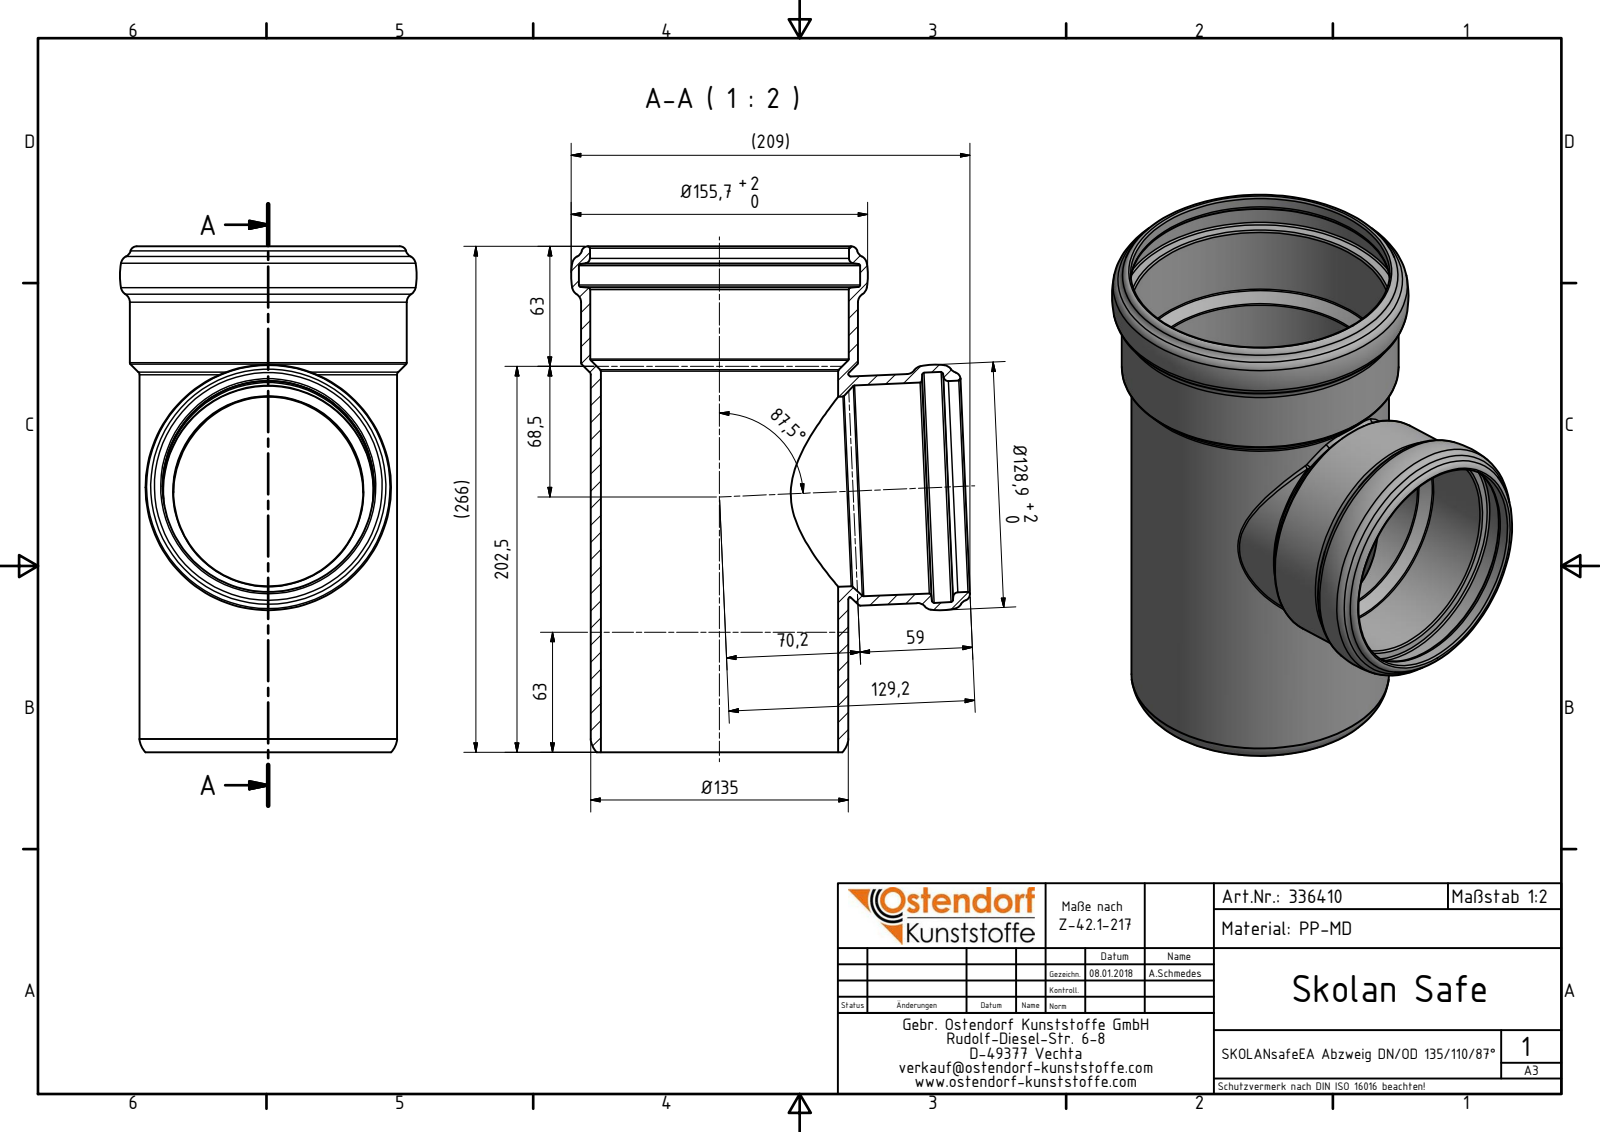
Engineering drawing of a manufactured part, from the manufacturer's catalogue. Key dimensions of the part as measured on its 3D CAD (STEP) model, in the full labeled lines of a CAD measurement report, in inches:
Part name (STEP PRODUCT): 336410 SKOLANsafeEA Abzweiger DN_OD 135_110_87°
STEP written by: Autodesk Inventor 2016 (AUTOMOTIVE_DESIGN)
Units: inches
Bodies: 1 solid, 59 faces (1 planar, 13 cylindrical, 45 other)
Overall size (bounding box): 10.453 × 8.244 × 6.13
Volume: 41.09 in³ · Surface area: 423.7 in²
Round holes (diameter × count): ⌀3.925 ×1, ⌀4.362 ×1, ⌀4.37 ×1, ⌀4.76 ×1, ⌀4.909 ×1, ⌀5.346 ×1, ⌀5.358 ×1, ⌀5.815 ×1
Round bosses / shafts (diameter × count): ⌀5.724 ×1, ⌀5.327 ×1, ⌀4.74 ×1
Partial cylindrical surfaces — rounded edges, fillets, slot ends (radius × count): R2.171 ×1
